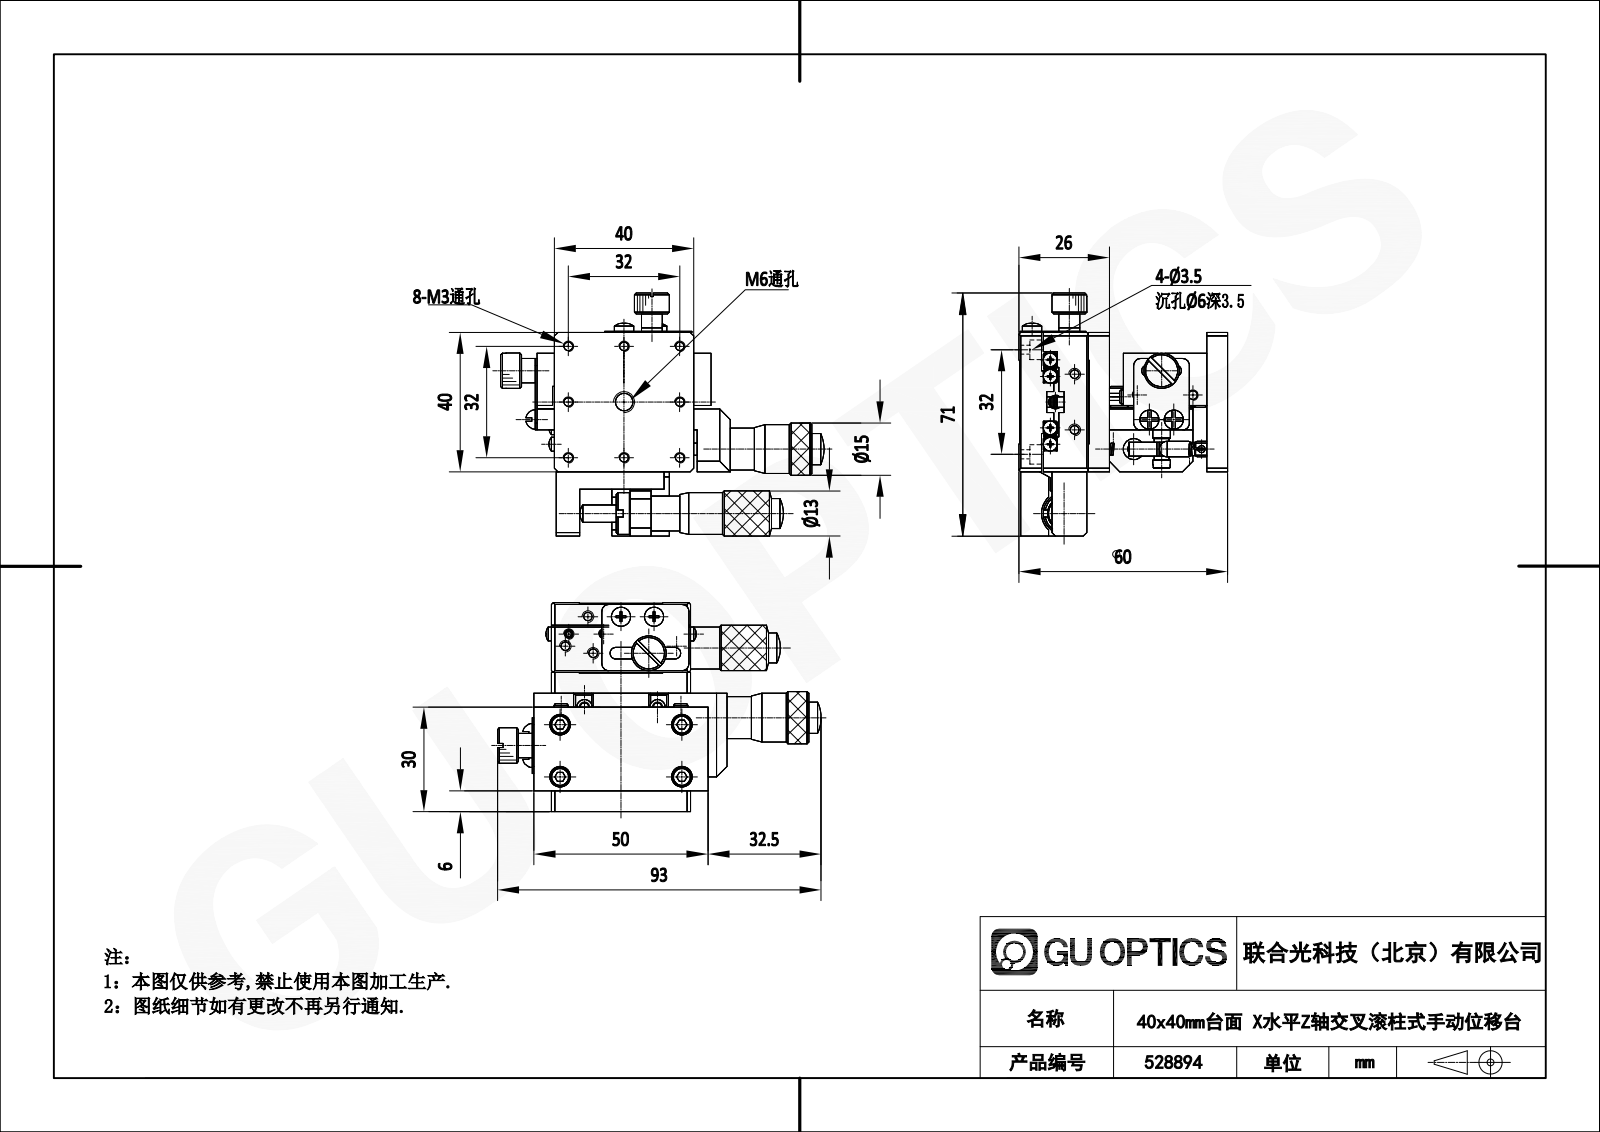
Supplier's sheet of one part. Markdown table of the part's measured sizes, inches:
| quantity | value |
| --- | --- |
| part name | 528894 |
| STEP written by | SolidWorks 2020 (CONFIG_CONTROL_DESIGN) |
| units | inches |
| bodies | 0 solids, 4704 faces (438 planar, 1058 cylindrical, 3208 other) |
| overall size | 3.921 × 2.952 × 2.362 |
| round holes (diameter × count) | 0.097 × 12, 0.118 × 12, 0.079 × 10, 0.062 × 9, 0.097 × 9, 0.065 × 8, 0.098 × 8, 0.177 × 8, 0.236 × 8, 0.126 × 6, 0.197 × 6, 0.11 × 4 |
| round bosses / shafts (diameter × count) | 0.157 × 6, 0.118 × 6, 0.236 × 3, 0.513 × 2, 0.474 × 2, 0.394 × 2, 0.354 × 2, 0.25 × 2 |
| partial cylindrical surfaces (radius × count) | 0.039 × 6, 0.079 × 5, 0.004 × 4, 0.295 × 3, 0.049 × 2, 0.067 × 2, 0.315 × 2, 0.157 × 1 |
| main face-to-face distances | 0.276, 0.236, 1.575, 0.512, 0.256, 1.339, 0.492, 0.531, 0.374, 0.02 |
| hole center spacings | 0.63, 0.394, 0.406, 0.891, 1.409, 0.256, 1.26, 1.185 |
